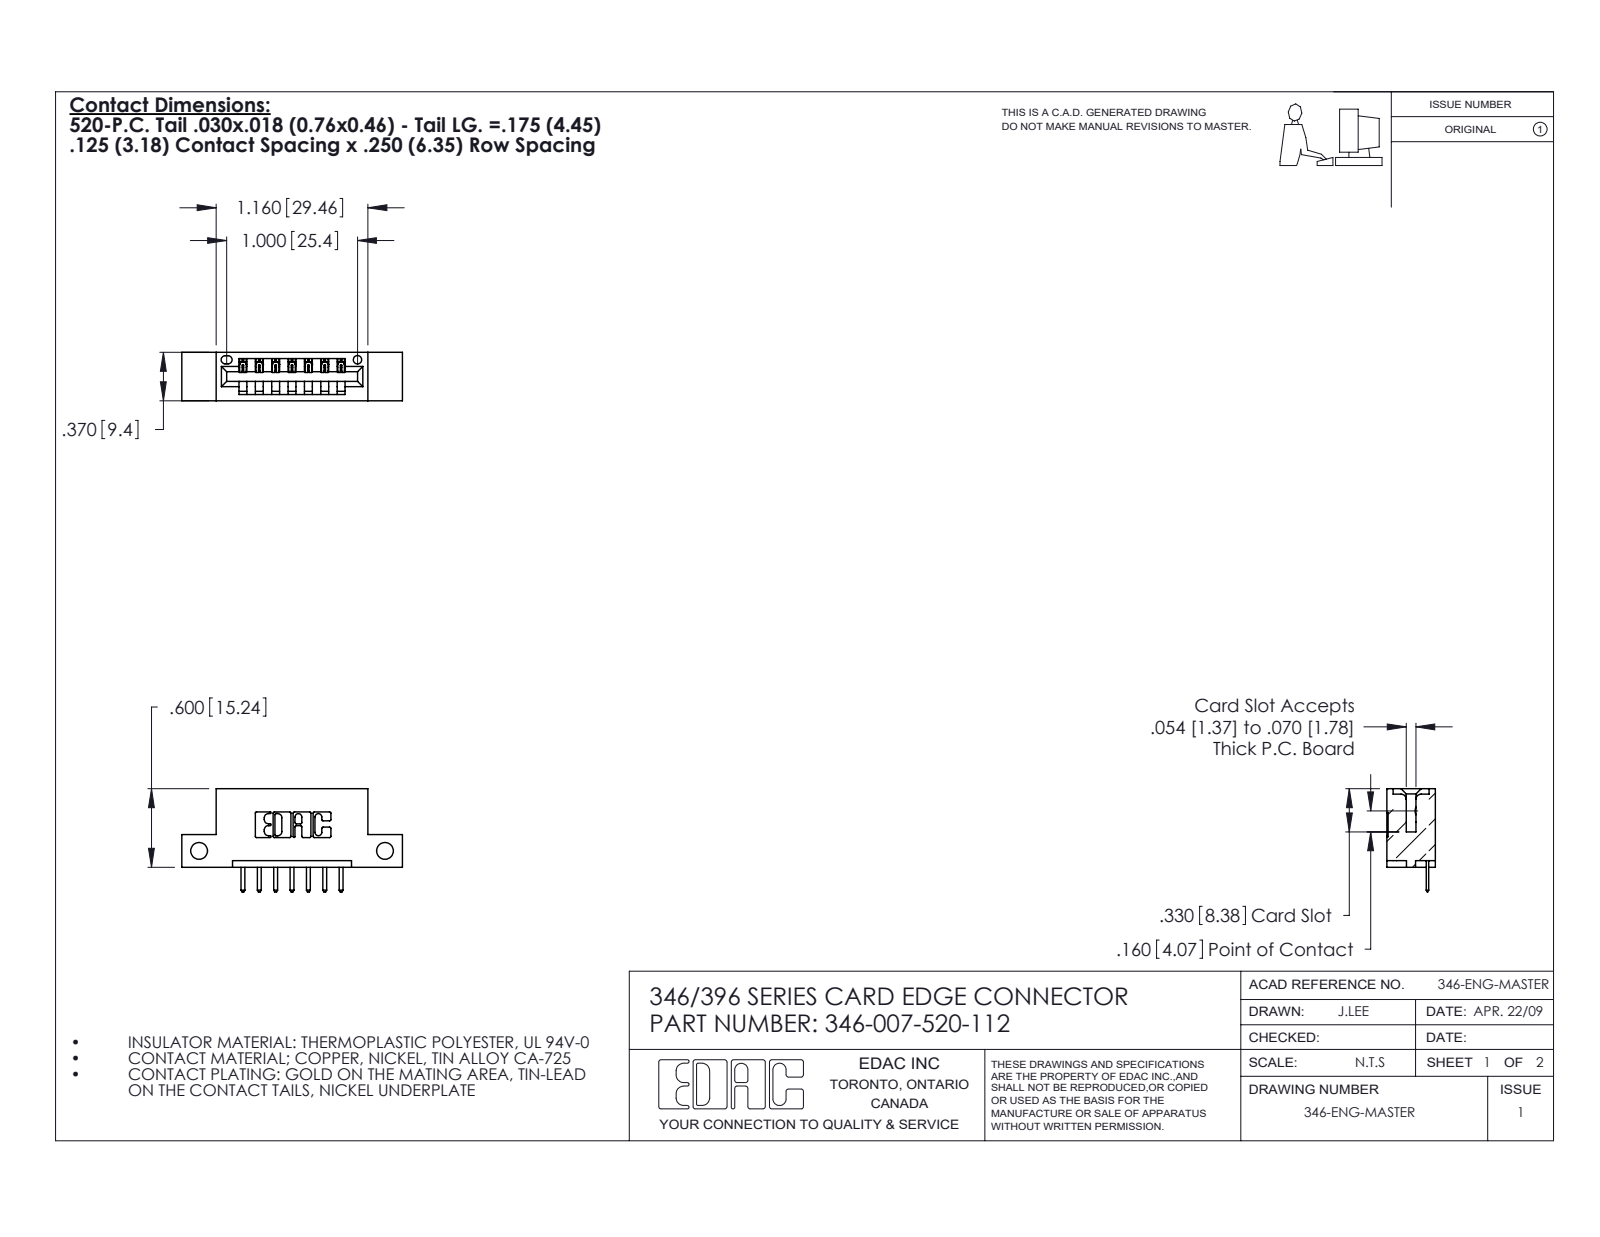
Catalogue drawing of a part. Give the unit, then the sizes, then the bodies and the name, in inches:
Units: inches
Overall size (bounding box): 1.685 × 0.788 × 0.37
Round holes (diameter × count): ⌀0.128 ×2, ⌀0.064 ×1
Partial cylindrical surfaces — rounded edges, fillets, slot ends (radius × count): R0.01 ×22, R0.01 ×16, R0.006 ×14, R0.007 ×6, R0.031 ×6, R0.026 ×3, R0.031 ×2, R0.04 ×2
Main face-to-face distances: 0.25, 0.37, 0.048, 0.322, 0.148, 0.222, 0.1, 0.174, 0.125, 0.185
Hole centre spacings: 1.42
Volume: 0.229 in³ · Surface area: 6.346 in²
Bodies: 8 solids, 556 faces (370 planar, 186 cylindrical, 0 other)
Part name (STEP PRODUCT): 346 Part_Flush Mounting Lugs - Side Mount; 346-007-520-112; 345-292-001_345-293-120
STEP written by: SolidWorks 2020 (CONFIG_CONTROL_DESIGN)
